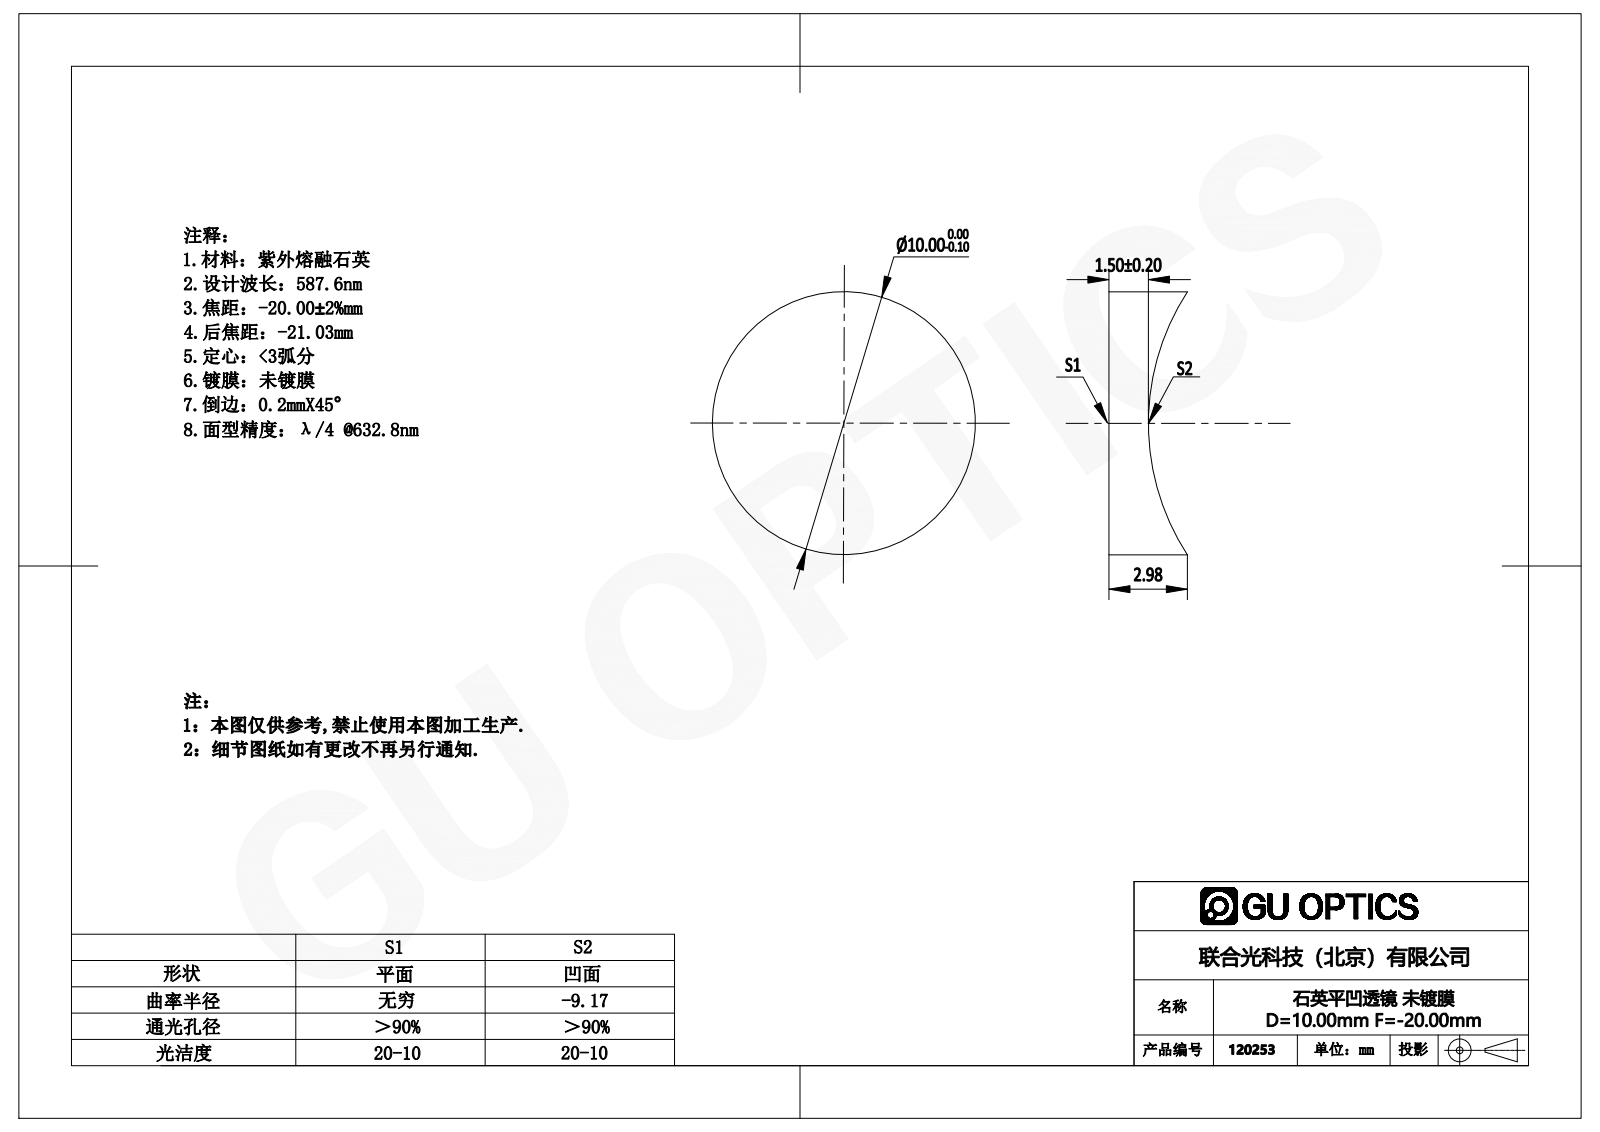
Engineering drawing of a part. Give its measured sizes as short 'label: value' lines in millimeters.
name: 120253
written by: SolidWorks 2016 (AUTOMOTIVE_DESIGN)
unit: mm
bodies: 1 solid, 5 faces (1 planar, 2 cylindrical, 2 other)
size: 10 × 10 × 2.98
volume: 174 mm³; area: 258 mm²
bosses: 1× ⌀10
